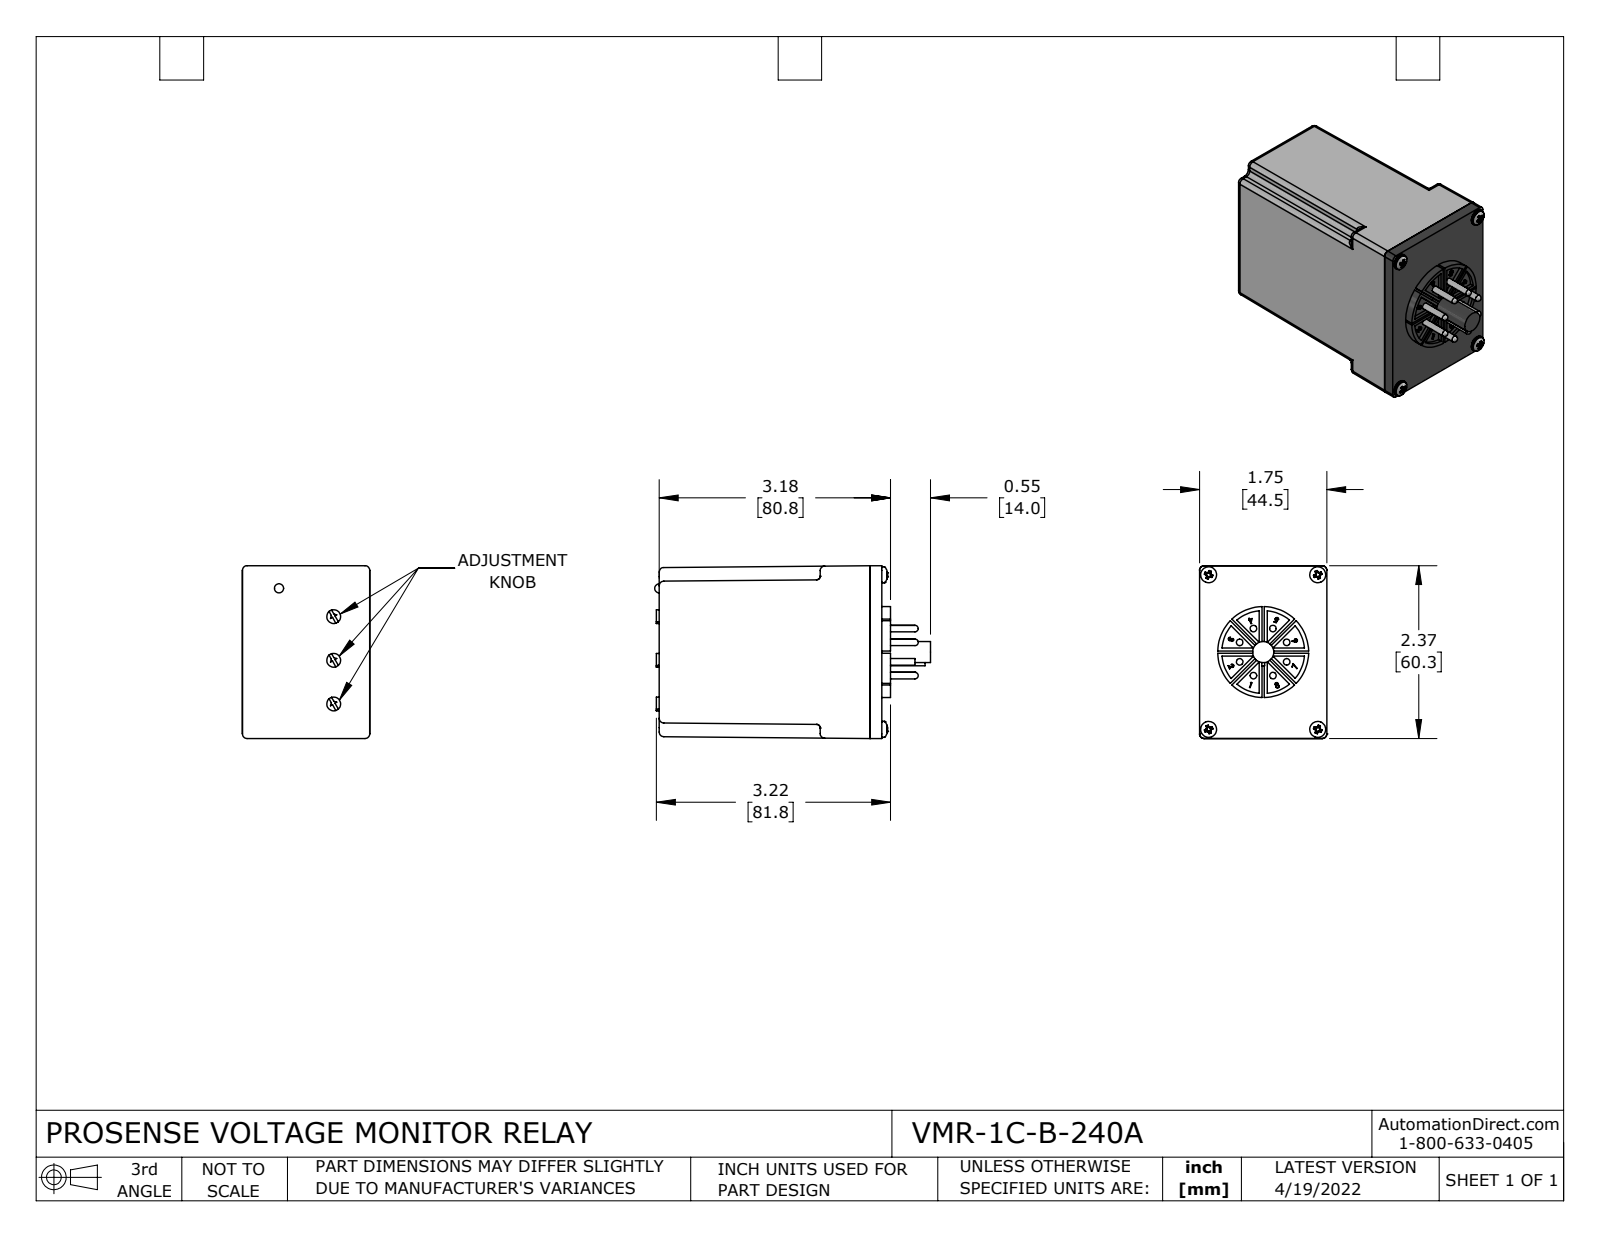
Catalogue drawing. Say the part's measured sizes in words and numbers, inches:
The part is named "VMR-1C-B-240A". Its 3-D file was written by "SolidWorks 2021 (CONFIG_CONTROL_DESIGN)". It is 18 solids with 574 faces: 249 planar, 170 cylindrical and 155 other. Overall it measures 3.79 by 2.375 by 1.75 inches. Its volume is 12.25 cubic inches and its surface area 44.71 square inches. Round holes: 4 of diameter 0.125. Round bosses or shafts: 8 of diameter 0.09, 4 of diameter 0.219, 3 of diameter 0.19, 1 of diameter 1.25, 1 of diameter 0.29. Partial cylindrical surfaces (rounded edges, fillets, slot ends): 32 of radius 0.063, 8 of radius 0.005, 4 of radius 0.05, 1 of radius 0.57. The main face-to-face distances are 2.9, 0.16, 3.06, 0.07, 0.23, 3.13, 0.188, 0.05, 0.12, 0.28. The hole center spacings are 1.5, 2.125, 2.601.
